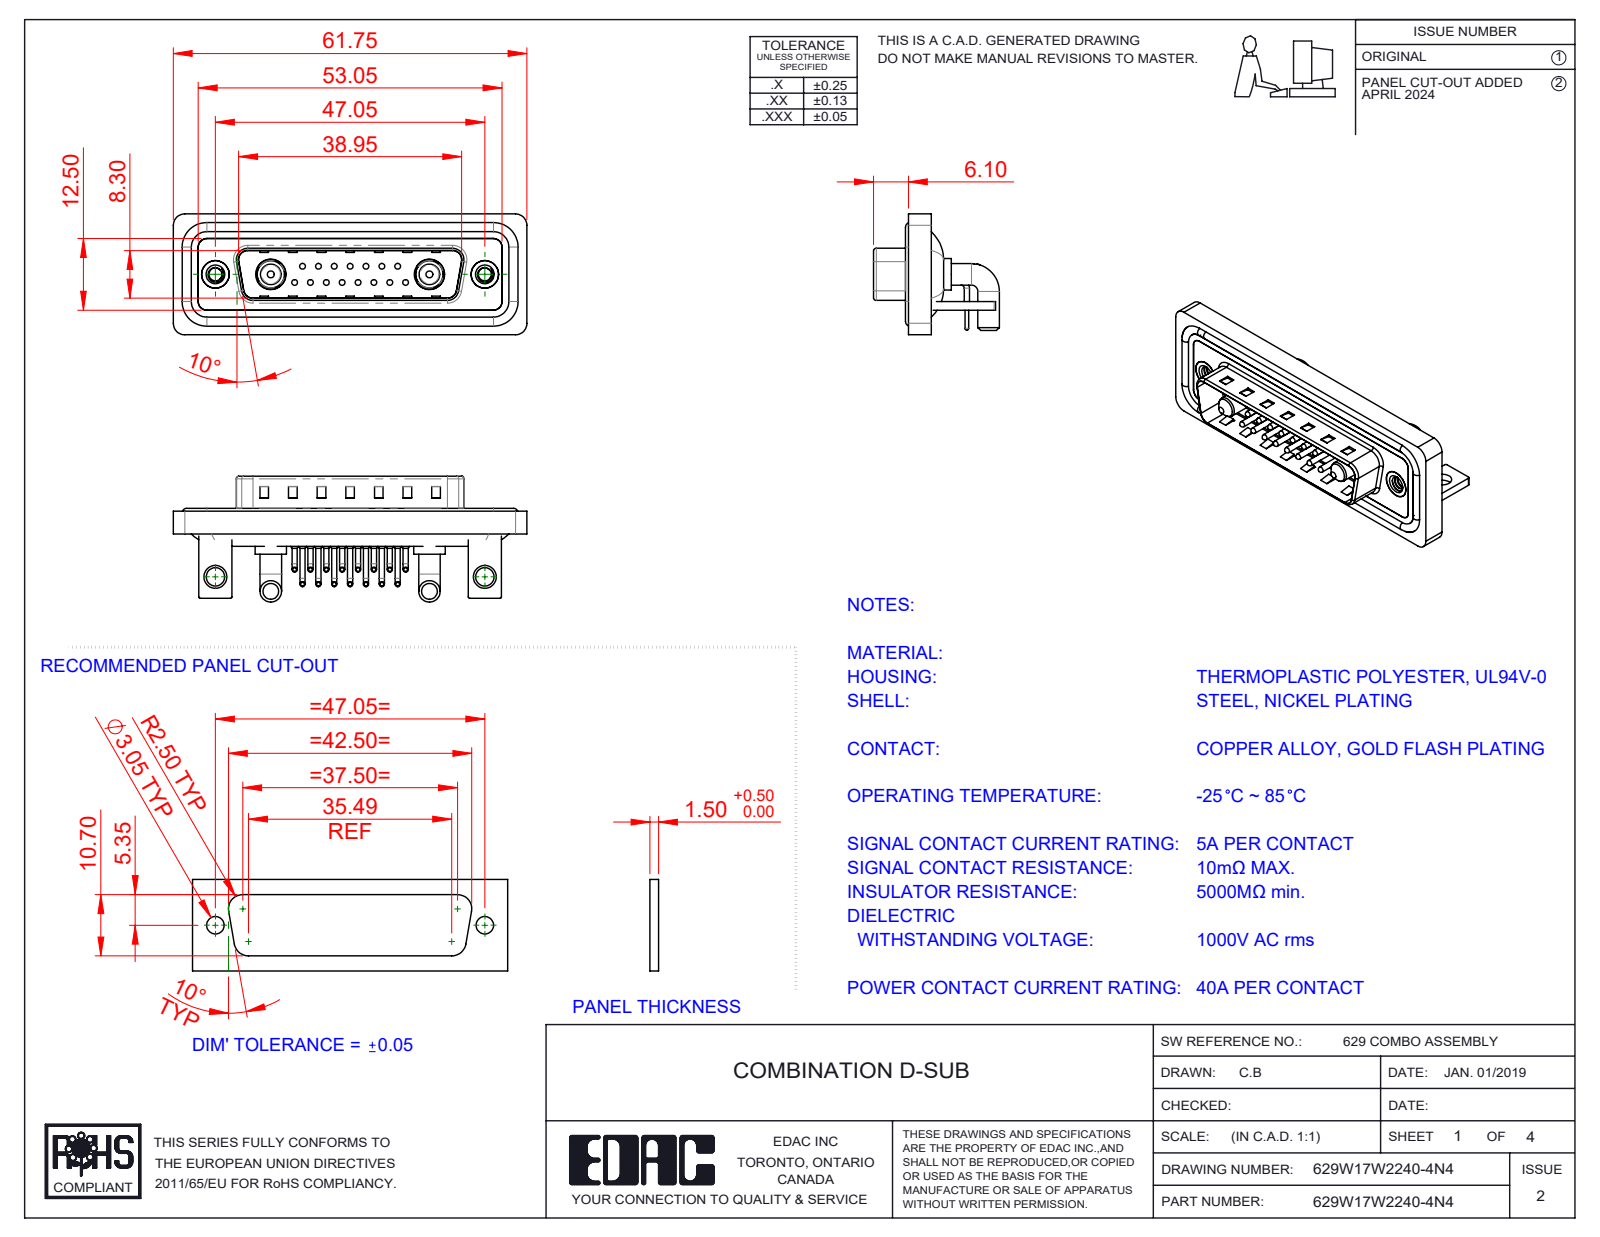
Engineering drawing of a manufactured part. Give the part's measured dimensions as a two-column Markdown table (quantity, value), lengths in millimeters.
| quantity | value |
| --- | --- |
| part name | Power Pin_40A RA; 629Combo Housing_17W2; 629Combo Waterproof Housing_25 Contacts; 629Combo Shell Rear_25 Contacts (+6 more) |
| STEP written by | SolidWorks 2023 (CONFIG_CONTROL_DESIGN) |
| units | millimeters |
| bodies | 28 solids, 2259 faces (1209 planar, 788 cylindrical, 262 other) |
| overall size | 61.75 × 21.98 × 21.1 |
| volume | 7 936 mm³ |
| surface area | 13 276 mm² |
| round holes (diameter × count) | 0.75 × 15, 1.6 × 15, 2 × 15, 2.26 × 2, 3.2 × 2, 4 × 2, 4.8 × 2, 4.85 × 2, 5 × 2, 5.3 × 2 |
| round bosses / shafts (diameter × count) | 0.9 × 30, 1.5 × 15, 1 × 15, 0.65 × 15, 3.75 × 4, 1.6 × 4, 5.5 × 2, 5.2 × 2 |
| partial cylindrical surfaces (radius × count) | 2 × 19, 1.5 × 18, 0.25 × 16, 1.01 × 15, 0.5 × 9, 1.6 × 8, 0.6 × 4, 0.65 × 4 |
| main face-to-face distances | 0.4, 0.8, 2.1, 1.5, 2.9, 1.1, 4.1, 1.6, 4.5, 3.7 |
| hole center spacings | 3.16, 2.77, 5.54, 8.31, 5.04, 7.49, 11.08, 5.03 |
